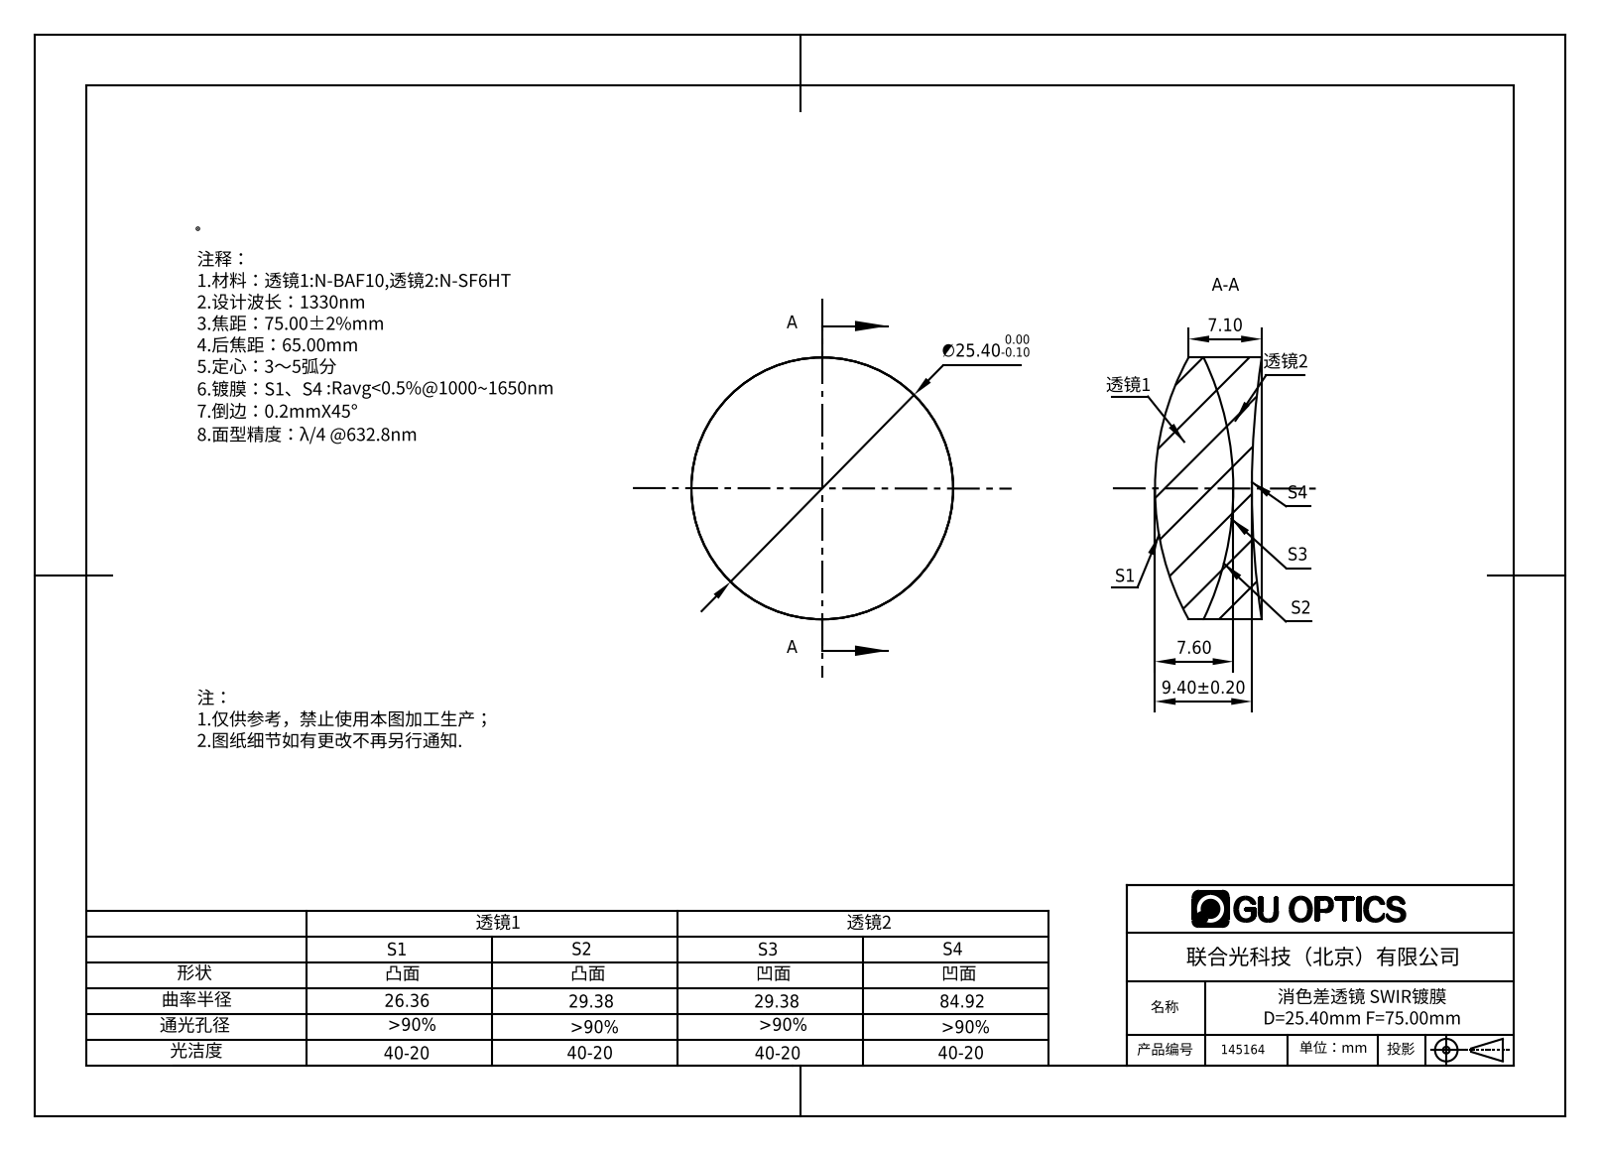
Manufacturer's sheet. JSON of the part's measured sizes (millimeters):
{"part_name": "145164", "step_written_by": "SolidWorks 2016 (AUTOMOTIVE_DESIGN)", "units": "millimeters", "bodies": {"solids": 2, "faces": 12, "planar": 0, "cylindrical": 4, "other": 8}, "overall_size": [25.4, 25.4, 10.36], "volume_mm3": 4197, "surface_area_mm2": 2682, "round_bosses_or_shafts": [[25.4, 1]]}
